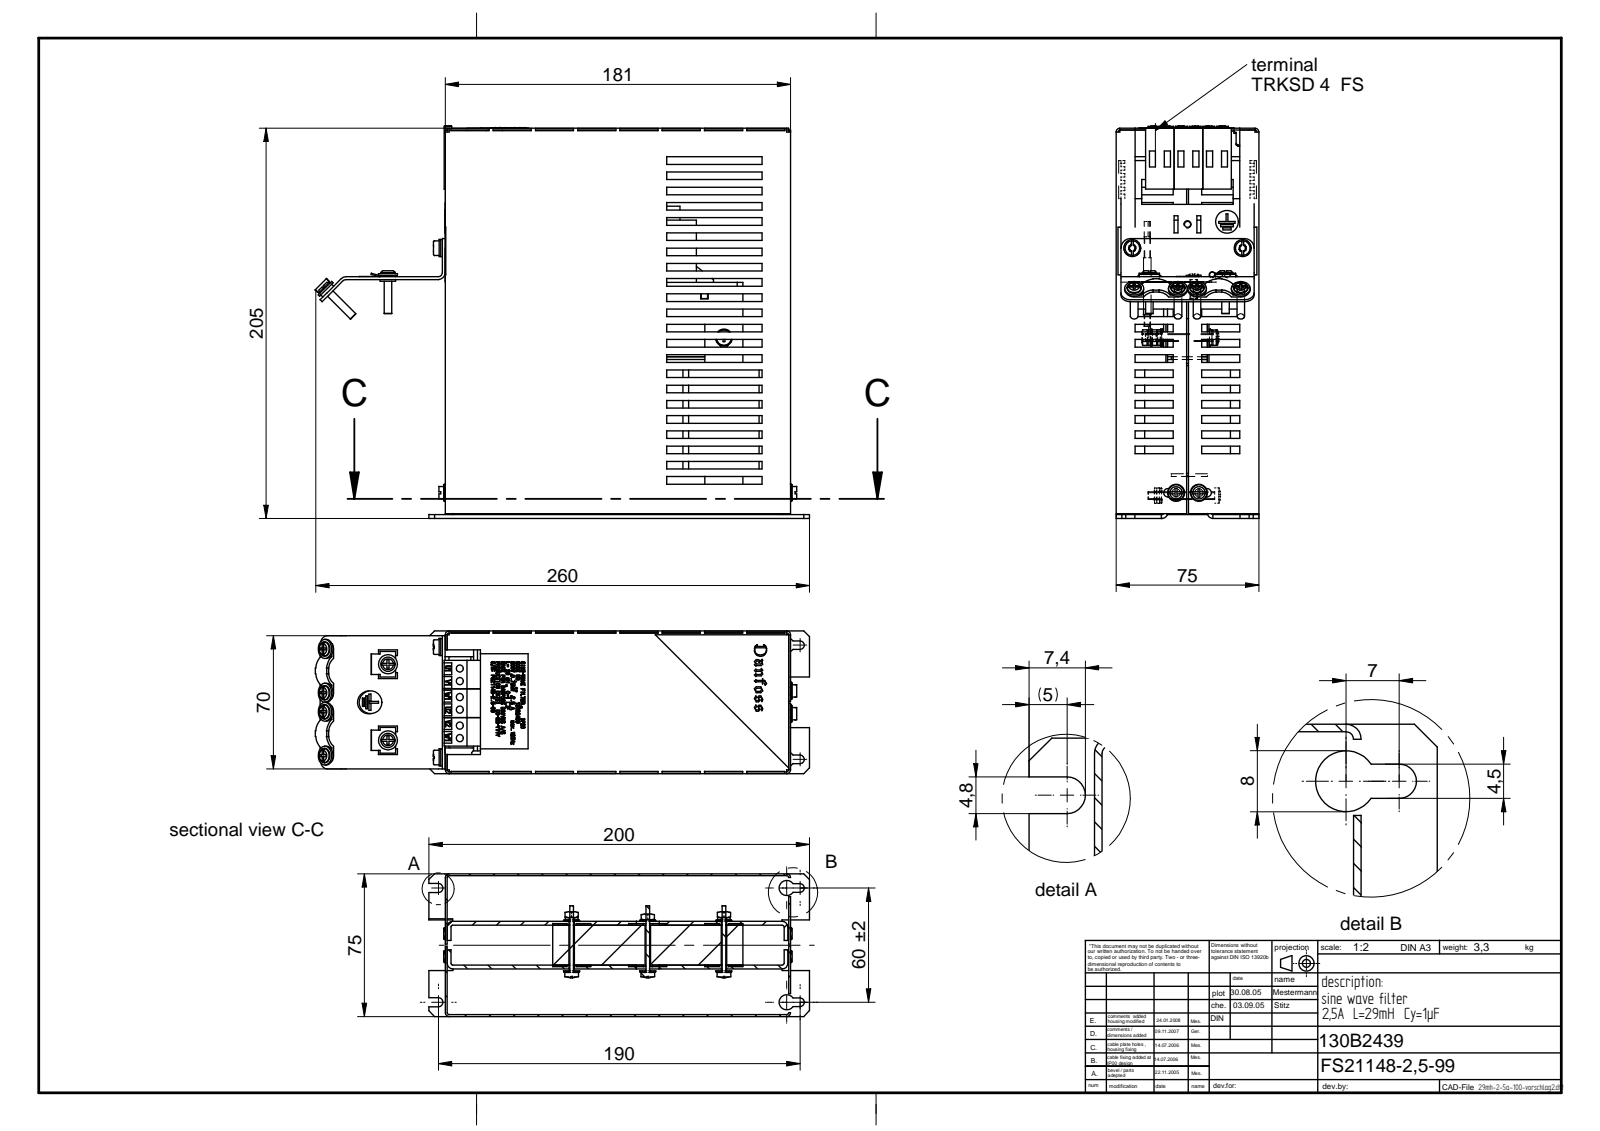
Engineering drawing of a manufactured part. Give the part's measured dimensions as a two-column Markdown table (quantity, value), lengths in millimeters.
| quantity | value |
| --- | --- |
| STEP written by | Unknown (CONFIG_CONTROL_DESIGN) |
| units | millimeters |
| bodies | 198 solids, 7974 faces (5493 planar, 1017 cylindrical, 1464 other) |
| overall size | 274.72 × 239 × 206.2 |
| volume | 1 592 000 mm³ |
| surface area | 1 155 000 mm² |
| round holes (diameter × count) | 3.3 × 34, 4.5 × 23, 4.3 × 13, 0.4 × 8, 3.24 × 8, 3.8 × 8, 3.2 × 6, 4.1 × 4, 8 × 4, 2.75 × 3, 4 × 3, 0.3 × 2 |
| round bosses / shafts (diameter × count) | 4 × 18, 9 × 12, 7.5 × 11, 8 × 9, 10 × 7, 8.8 × 4, 2.89 × 4, 12 × 3 |
| partial cylindrical surfaces (radius × count) | 3 × 86, 1 × 26, 0.8 × 23, 6 × 21, 2.25 × 20, 2.4 × 20, 2 × 18, 2.8 × 13 |
| main face-to-face distances | 1, 74, 10.5, 37.5, 36.5, 27, 48, 26, 47, 75 |
| hole center spacings | 23, 33, 4, 30, 40, 27.42, 10, 56 |
